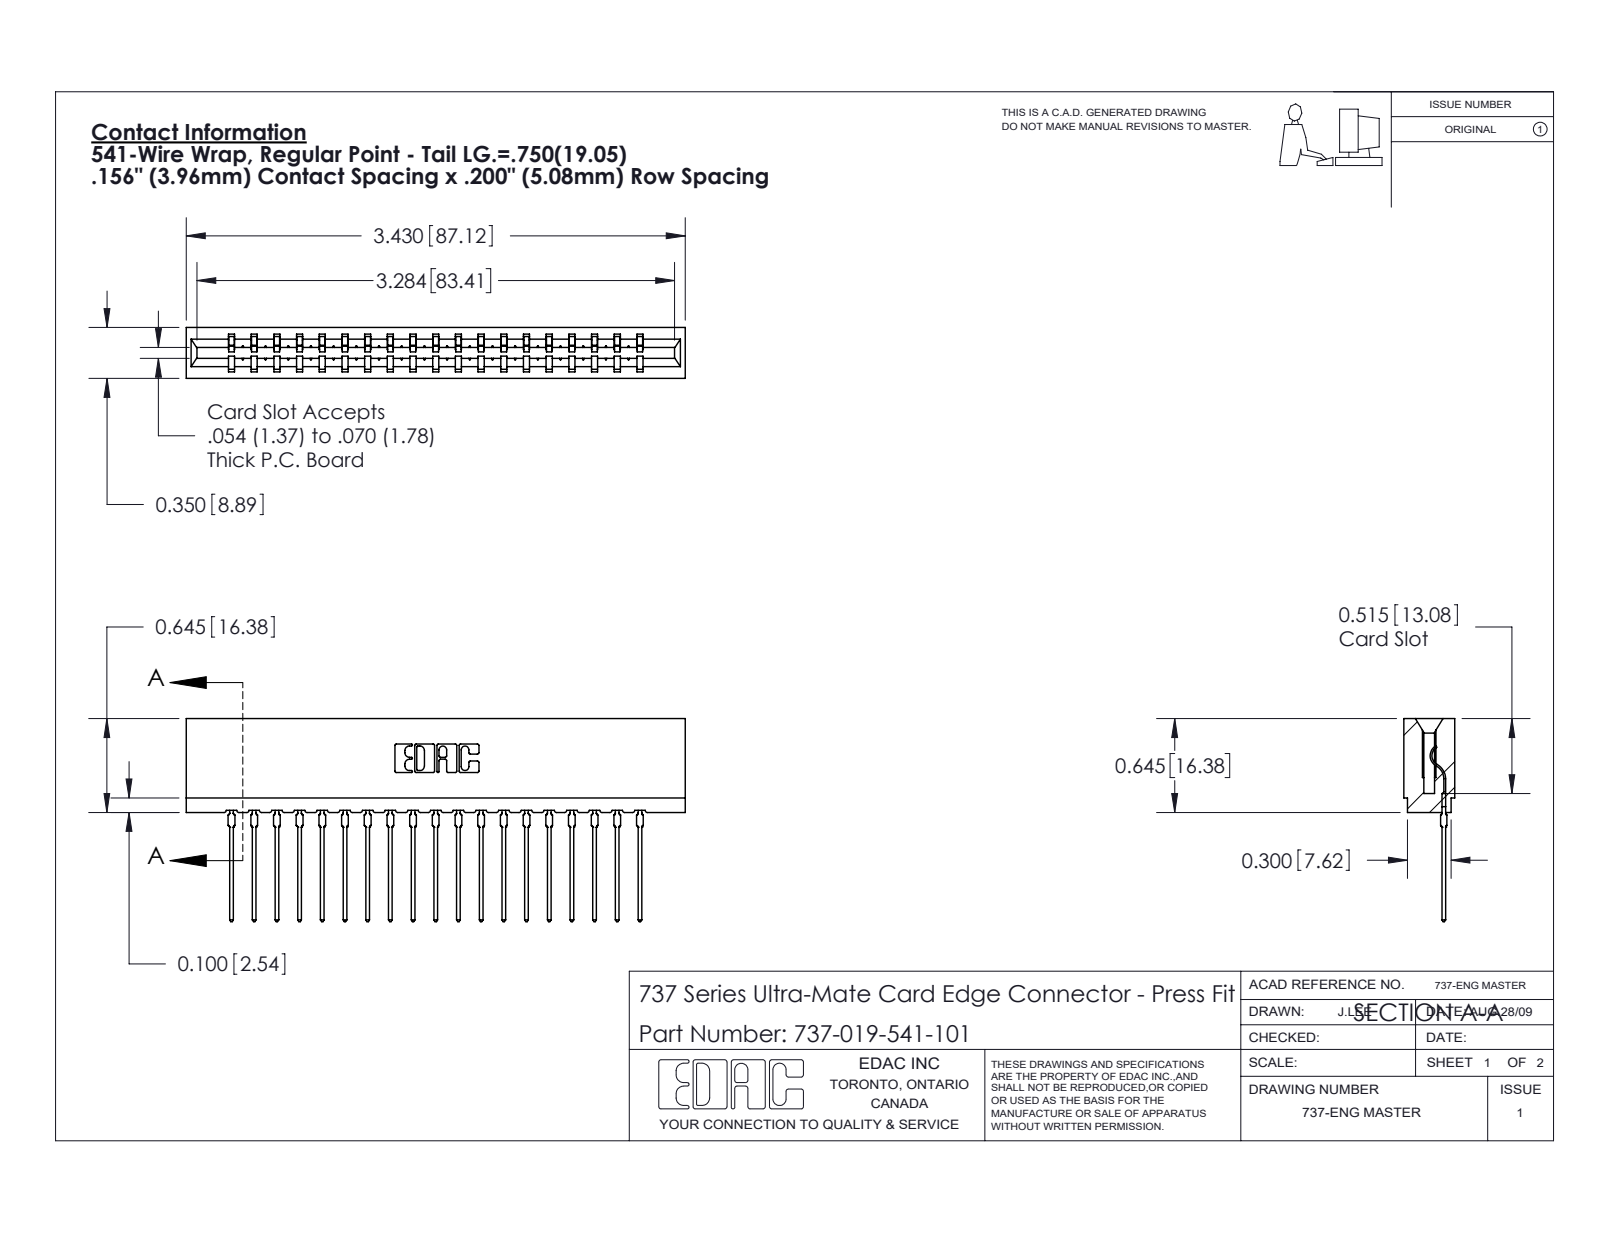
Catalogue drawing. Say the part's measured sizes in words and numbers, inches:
The part is named "745-292-001_541; 737 Part_Insulator Option - 01; 737-019-541-101". Its 3-D file was written by "SolidWorks 2020 (CONFIG_CONTROL_DESIGN)". It is 20 solids with 2241 faces: 1346 planar, 401 cylindrical and 494 other. Overall it measures 3.43 by 1.396 by 0.35 inches. Its volume is 0.529 cubic inches and its surface area 18.02 square inches. Partial cylindrical surfaces (rounded edges, fillets, slot ends): 38 of radius 0.015, 38 of radius 0.021, 22 of radius 0.01, 6 of radius 0.007, 6 of radius 0.031, 4 of radius 0.005, 4 of radius 0.011, 3 of radius 0.026. The main face-to-face distances are 0.138, 0.212, 0.35, 0.156, 0.624, 0.78, 0.468, 0.074, 0.312, 1.404.
